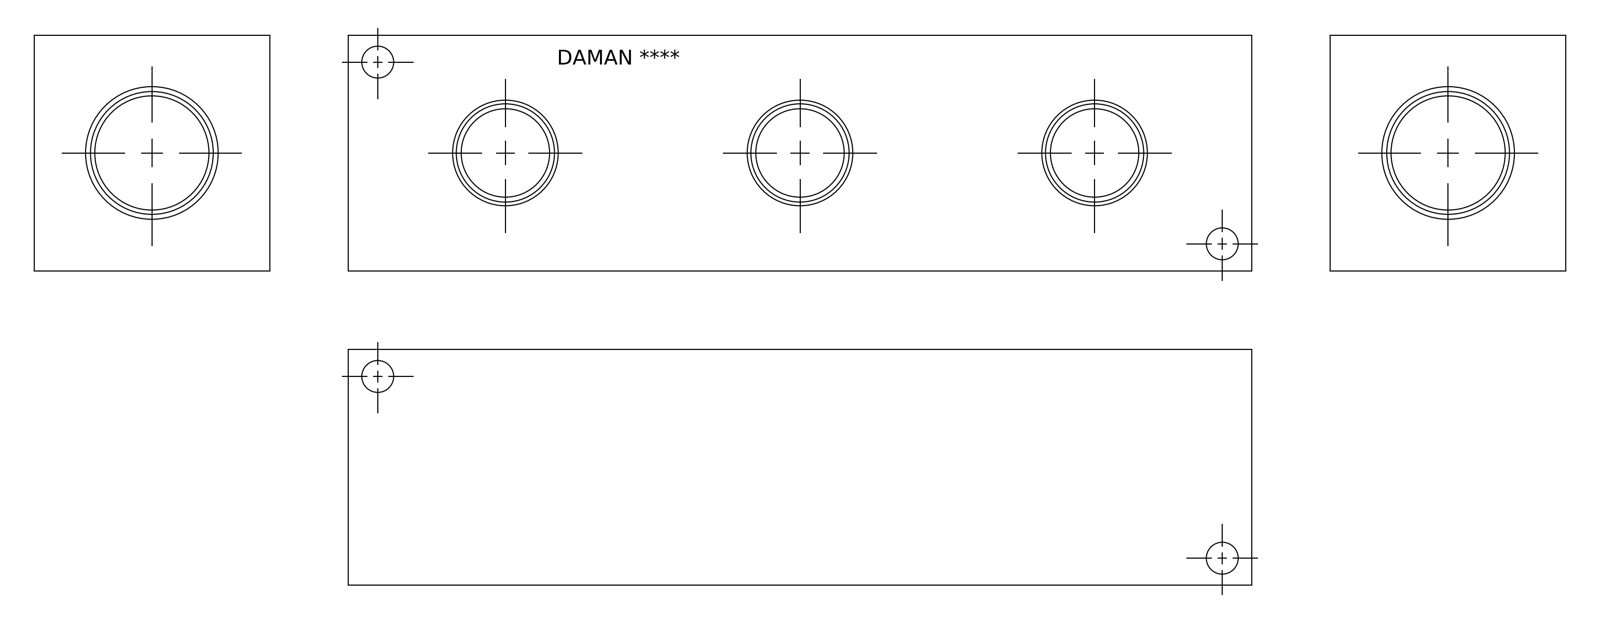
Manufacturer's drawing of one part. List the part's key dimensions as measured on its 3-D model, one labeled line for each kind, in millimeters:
Part name (STEP PRODUCT): Part_AH0000316P.C13731R0_3D
STEP written by: Autodesk Inventor 2019 (AUTOMOTIVE_DESIGN)
Units: millimetres
Bodies: 1 solid, 346 faces (220 planar, 18 cylindrical, 108 other)
Overall size (bounding box): 292.1 × 76.2 × 76.2
Volume: 1 549 000 mm³ · Surface area: 121 763 mm²
Round holes (diameter × count): ⌀10.31 ×4, ⌀28.57 ×3, ⌀33.71 ×3, ⌀36.91 ×1, ⌀42.47 ×1
Main face-to-face distances: 76.2, 292.1, 57.2, 19, 19.51, 272.59, 253.08, 75.2, 18, 1
Hole centre spacings: 50.65, 95.25, 139.64, 233.62, 279.28, 190.5
